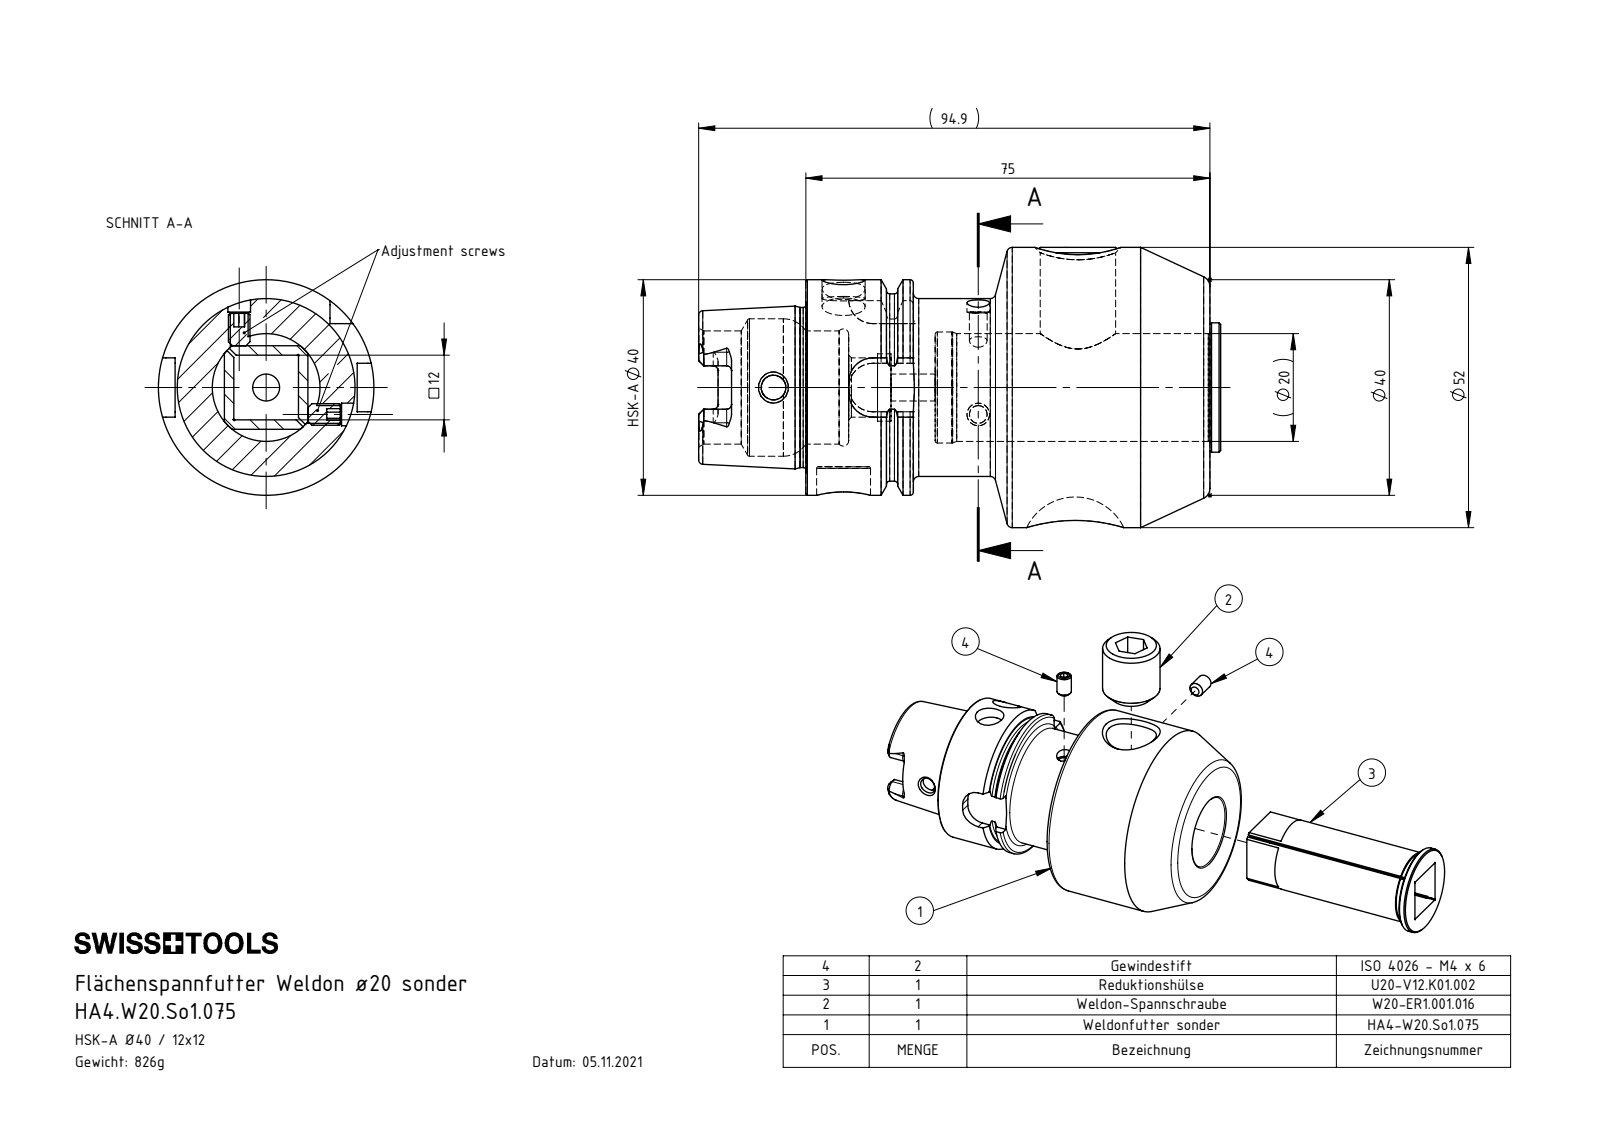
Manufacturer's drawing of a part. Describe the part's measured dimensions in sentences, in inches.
The part is named "U20-V12.K01.002_A; W20-ER1.001.016; HA4-W20.So1.075_A_Fertigbearbeitung; ISO 4026 - M4 x 6 (+1 more)". Its 3-D file was written by "SolidWorks 2017 (AUTOMOTIVE_DESIGN)". It is 5 solids with 225 faces: 112 planar, 49 cylindrical and 64 other. Overall it measures 3.815 by 2.047 by 2.047 inches. Its volume is 6.431 cubic inches and its surface area 48.13 square inches. Round holes: 2 of diameter 0.13, 2 of diameter 0.165, 2 of diameter 0.315, 1 of diameter 0.181, 1 of diameter 0.197, 1 of diameter 0.394, 1 of diameter 0.433, 1 of diameter 0.492, 1 of diameter 0.551, 1 of diameter 0.811, 1 of diameter 0.827, 1 of diameter 1.004. Round bosses or shafts: 2 of diameter 0.157, 1 of diameter 2.047, 1 of diameter 1.575, 1 of diameter 1.368, 1 of diameter 1.299, 1 of diameter 1.17, 1 of diameter 0.945, 1 of diameter 0.787. Partial cylindrical surfaces (rounded edges, fillets, slot ends): 6 of radius 0.035, 4 of radius 0.074, 4 of radius 0.177. The main face-to-face distances are 0.472, 0.069, 0.541, 2.953, 0.079, 0.61, 0.945, 2.008, 3.031, 2.087. The hole center spacings are 0.754, 1.004, 1.509, 1.713.
